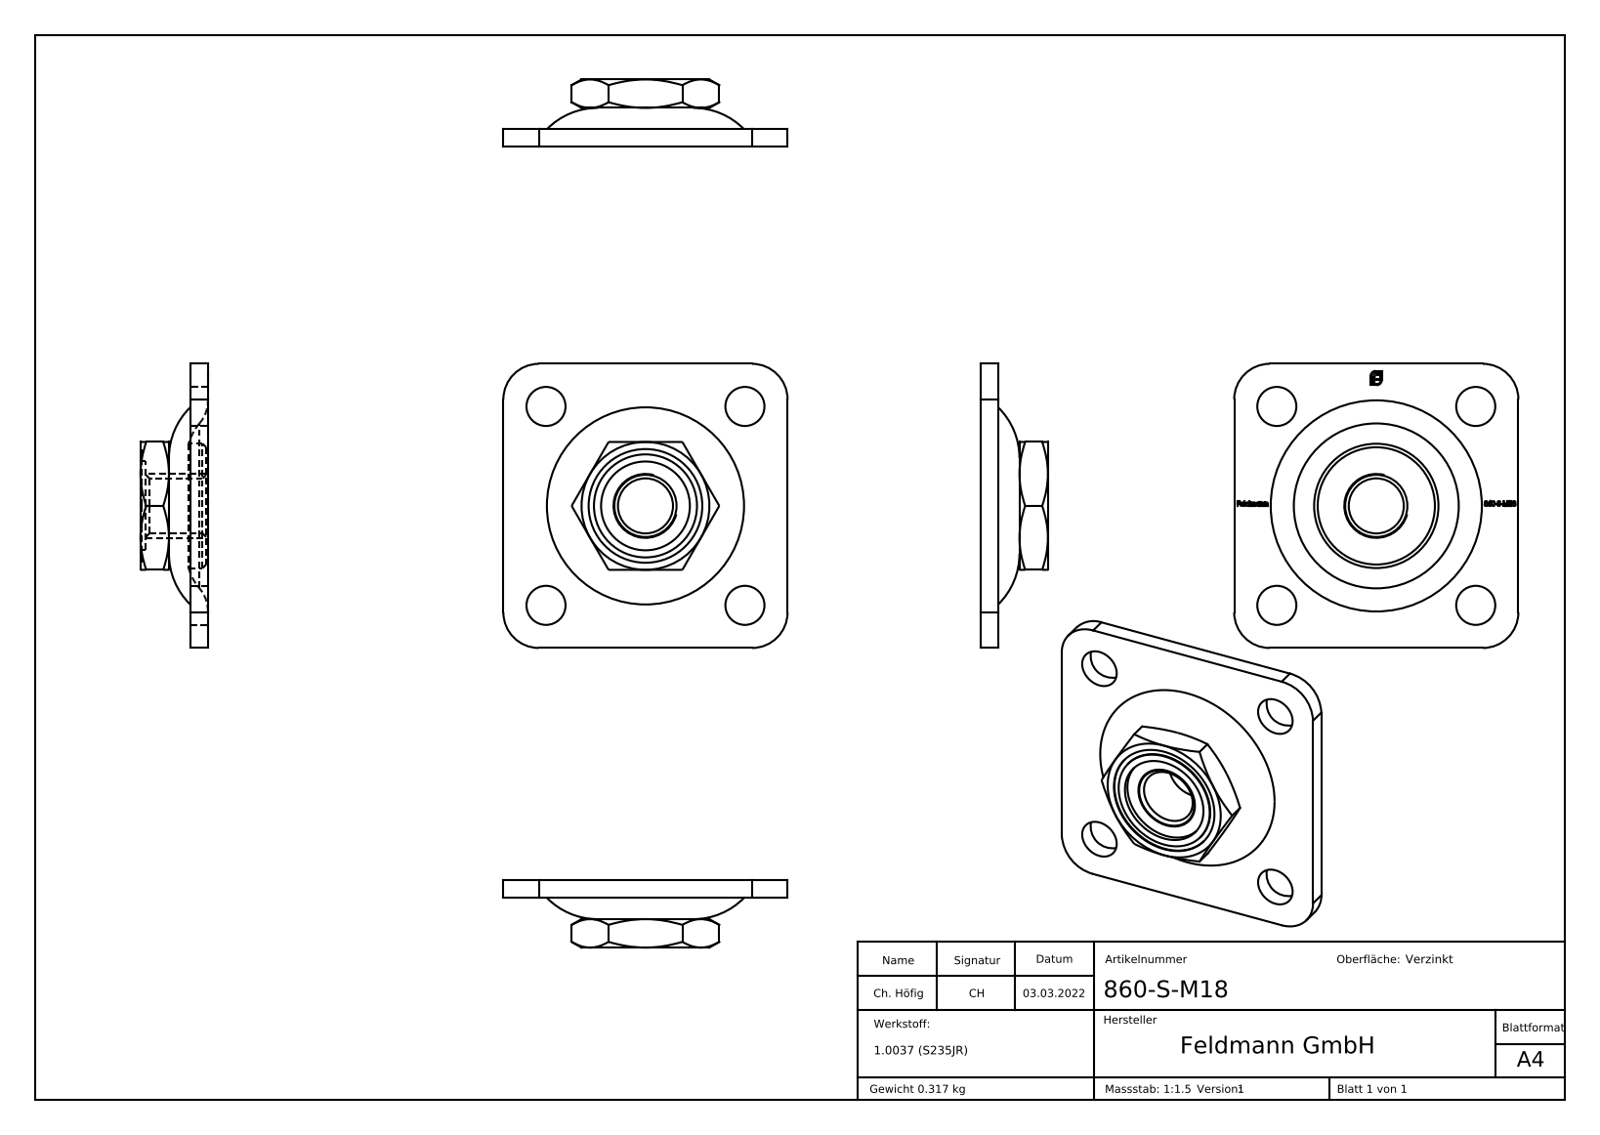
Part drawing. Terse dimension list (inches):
name: 860-S-M18
written by: SolidWorks 2018 (CONFIG_CONTROL_DESIGN)
unit: in
bodies: 1 solid, 319 faces (153 planar, 13 cylindrical, 153 other)
size: 3.15 × 3.15 × 0.748
volume: 2.481 in³; area: 27.25 in²
holes: 4× ⌀0.433, 1× ⌀0.61, 1× ⌀0.984, 1× ⌀1.26
bosses: 1× ⌀1.378, 1× ⌀1.142
rounds: 4× R0.394
face distances: 0.197, 0.02, 0.177, 3.15, 0.236, 0.433, 0.413, 1.417, 0.748, 0.728
hole spacings: 1.559, 2.205, 3.118
